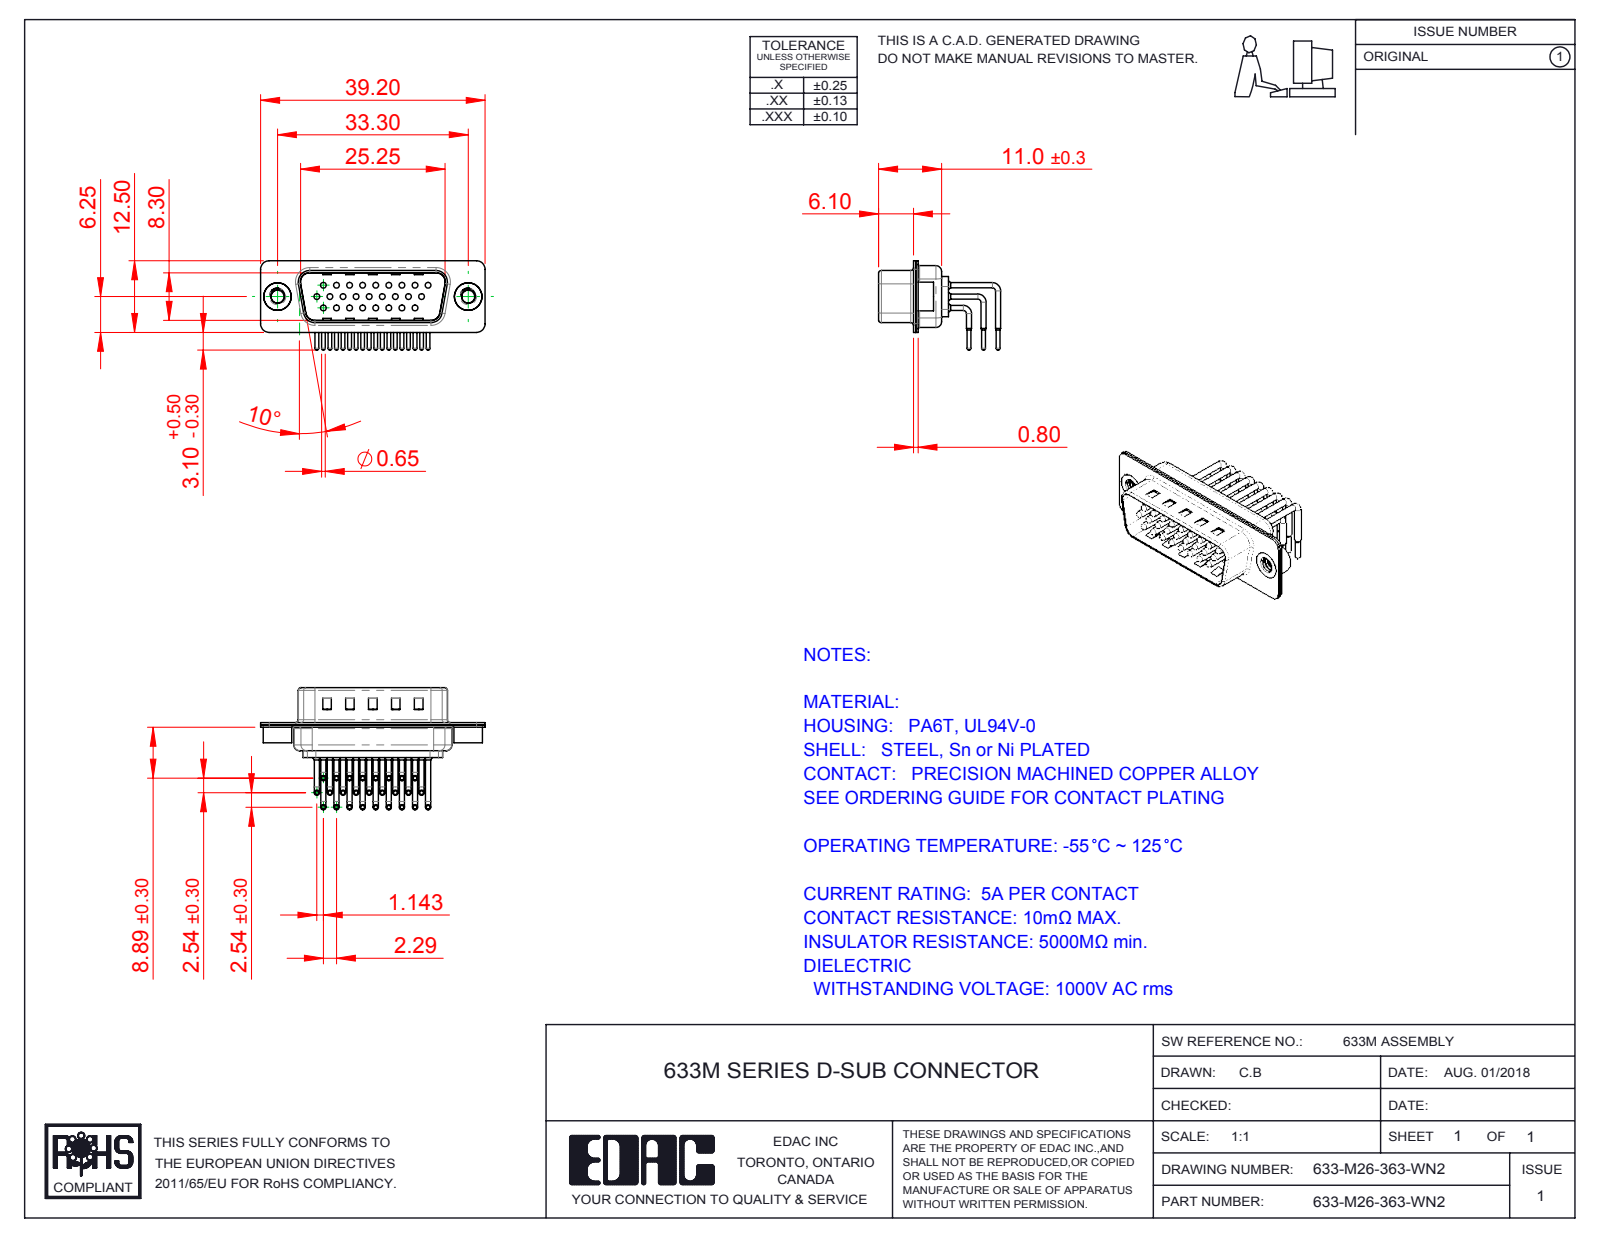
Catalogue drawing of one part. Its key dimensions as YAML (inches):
part_name: "633M 4-40 Threaded Rivet; 633-M26-363-WN2; 633M Shell Rear_26 Contacts; 633M Contact Row 3 (+4 more)"
step_written_by: "SolidWorks 2016 (CONFIG_CONTROL_DESIGN)"
units: inches
bodies: {solids: 31, faces: 3200, planar: 1803, cylindrical: 1069, other: 328}
overall_size: [1.543, 0.839, 0.614]
volume: 0.128
surface_area: 10.38
round_holes:
  - {diameter: 0.039, count: 26}
  - {diameter: 0.067, count: 26}
  - {diameter: 0.079, count: 26}
  - {diameter: 0.089, count: 2}
  - {diameter: 0.157, count: 2}
  - {diameter: 0.189, count: 2}
round_bosses_or_shafts:
  - {diameter: 0.035, count: 52}
  - {diameter: 0.059, count: 26}
  - {diameter: 0.026, count: 26}
  - {diameter: 0.197, count: 2}
  - {diameter: 0.193, count: 2}
partial_cylinders:
  - {radius: 0.04, count: 26}
  - {radius: 0.059, count: 16}
  - {radius: 0.079, count: 12}
  - {radius: 0.02, count: 8}
  - {radius: 0.063, count: 8}
  - {radius: 0.01, count: 4}
  - {radius: 0.024, count: 4}
  - {radius: 0.026, count: 4}
face_to_face_distances: [0.016, 0.033, 0.376, 0.059, 0.343, 0.075, 0.049, 0.409, 0.031, 0.014]
hole_center_spacings: [0.156, 0.09, 0.18, 0.238, 0.09, 0.324, 0.27, 0.413]
